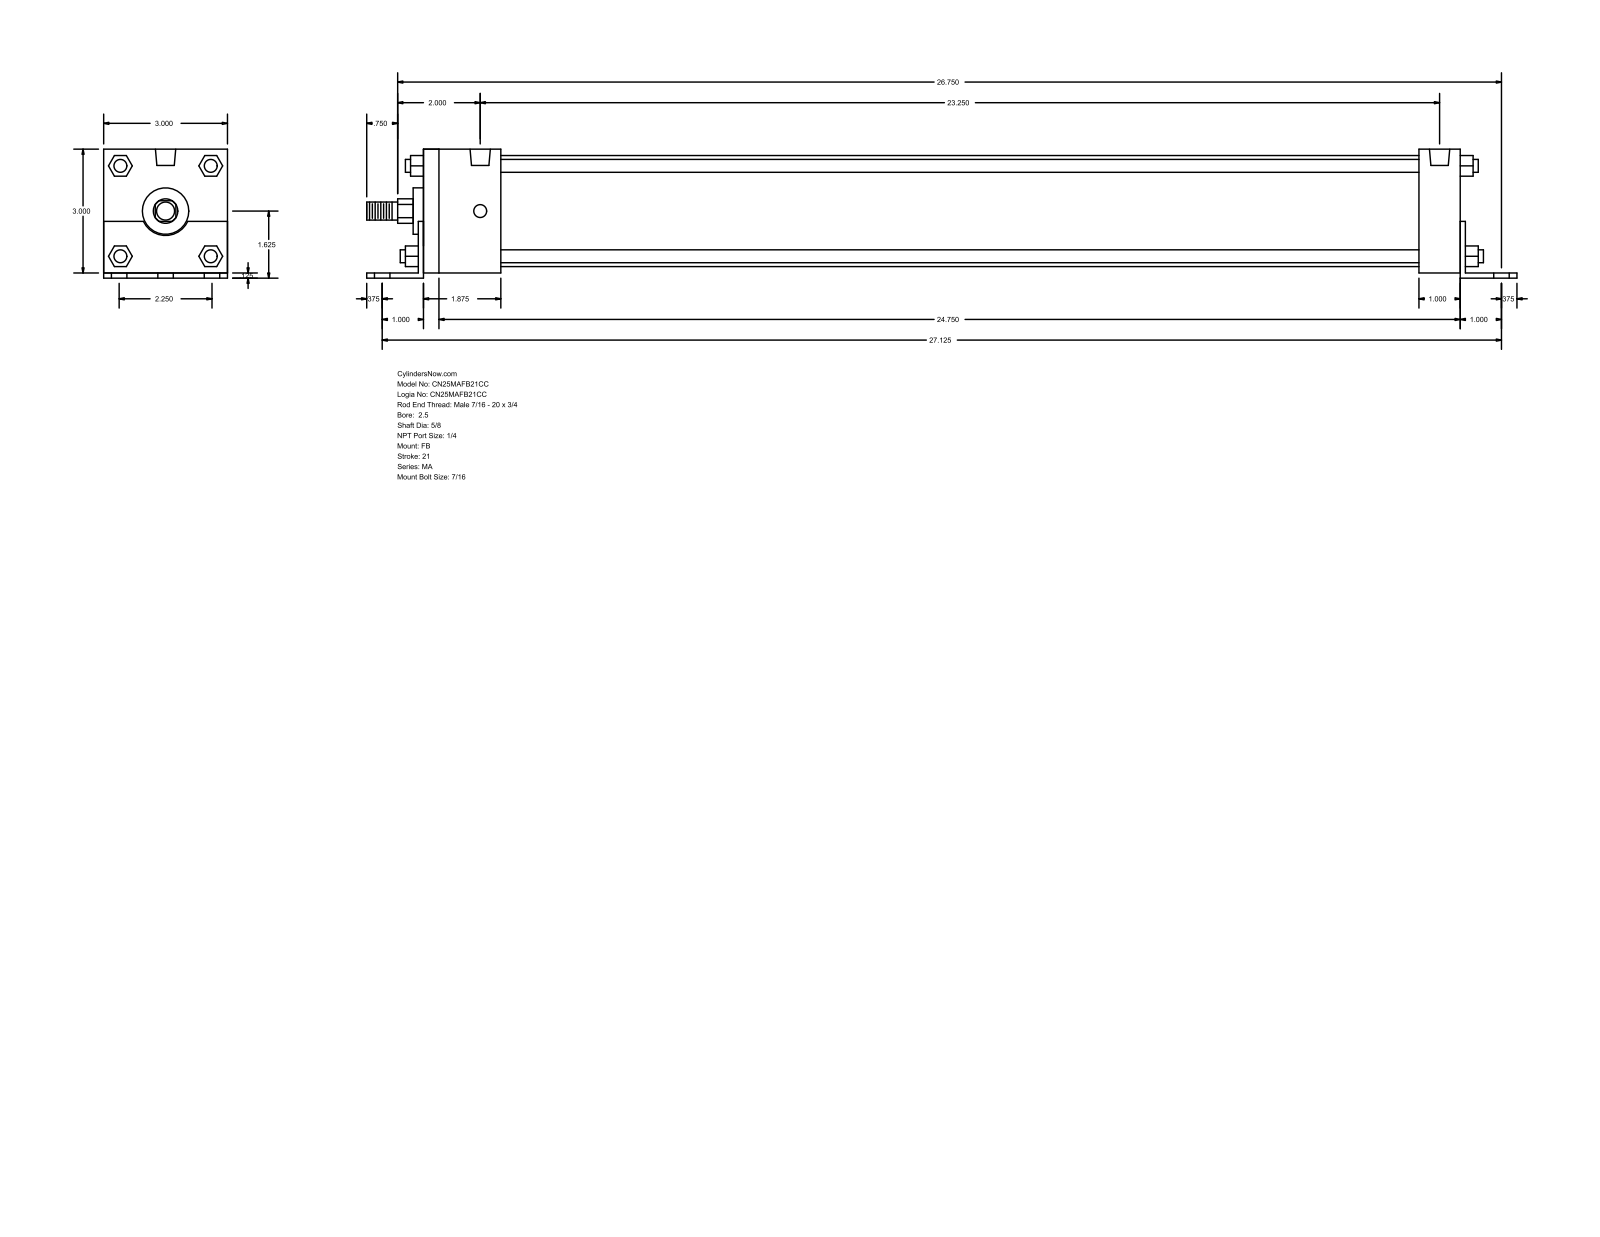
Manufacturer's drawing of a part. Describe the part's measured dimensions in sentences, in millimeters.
The part is named "MA_FB__0250_0.625". Its 3-D file was written by "GSSL Pune (CONFIG_CONTROL_DESIGN)". It is 0 solids with 140 faces: 105 planar, 35 cylindrical and 0 other. Overall it measures 708.02 by 79.38 by 76.2 millimeters. Round holes: 6 of diameter 11.11, 4 of diameter 7.94, 2 of diameter 12.49. Round bosses or shafts: 4 of diameter 7.94, 1 of diameter 68.33, 1 of diameter 28.57, 1 of diameter 15.88, 1 of diameter 11.11. Partial cylindrical surfaces (rounded edges, fillets, slot ends): 1 of radius 7.54, 1 of radius 15.05. The main face-to-face distances are 76.2, 3.17, 79.37, 3.18, 641.35, 638.17, 28.58, 47.62, 25.4, 644.53. The hole center spacings are 28.57, 689.57, 688.98, 47.62, 57.14, 66.75, 590.55, 629.3.
